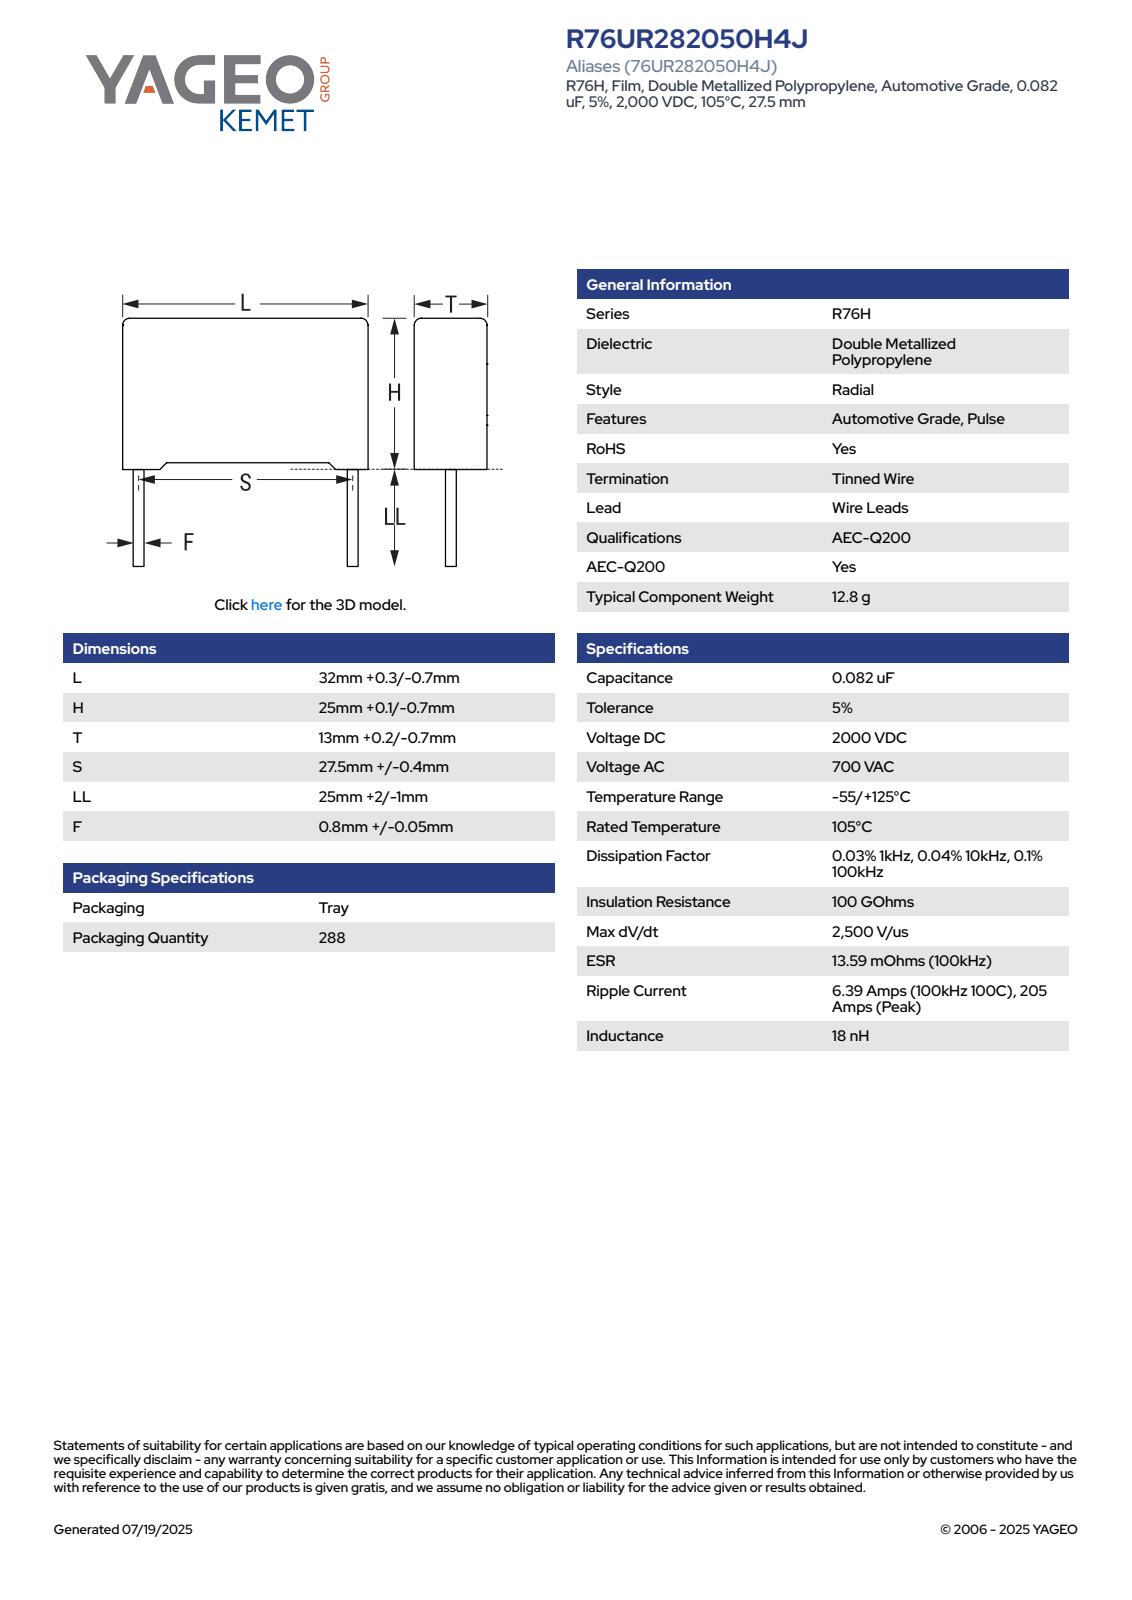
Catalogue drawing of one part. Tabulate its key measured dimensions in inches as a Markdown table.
| quantity | value |
| --- | --- |
| part name | CFR_RB2R76_32X25X13_L32.3H25.1T13.2S27.5LL27F0.85 |
| STEP written by | SolidWorks 2014 (AUTOMOTIVE_DESIGN) |
| units | inches |
| bodies | 4 solids, 85 faces (77 planar, 8 cylindrical, 0 other) |
| overall size | 2.051 × 1.272 × 0.52 |
| volume | 0.635 in³ |
| surface area | 5.163 in² |
| round bosses / shafts (diameter × count) | 0.033 × 2 |
| partial cylindrical surfaces (radius × count) | 0.02 × 4 |
| main face-to-face distances | 0.52, 1.272, 0.954, 0.959, 0.03, 0.034, 0.988, 0.043, 0.52, 1.229 |
